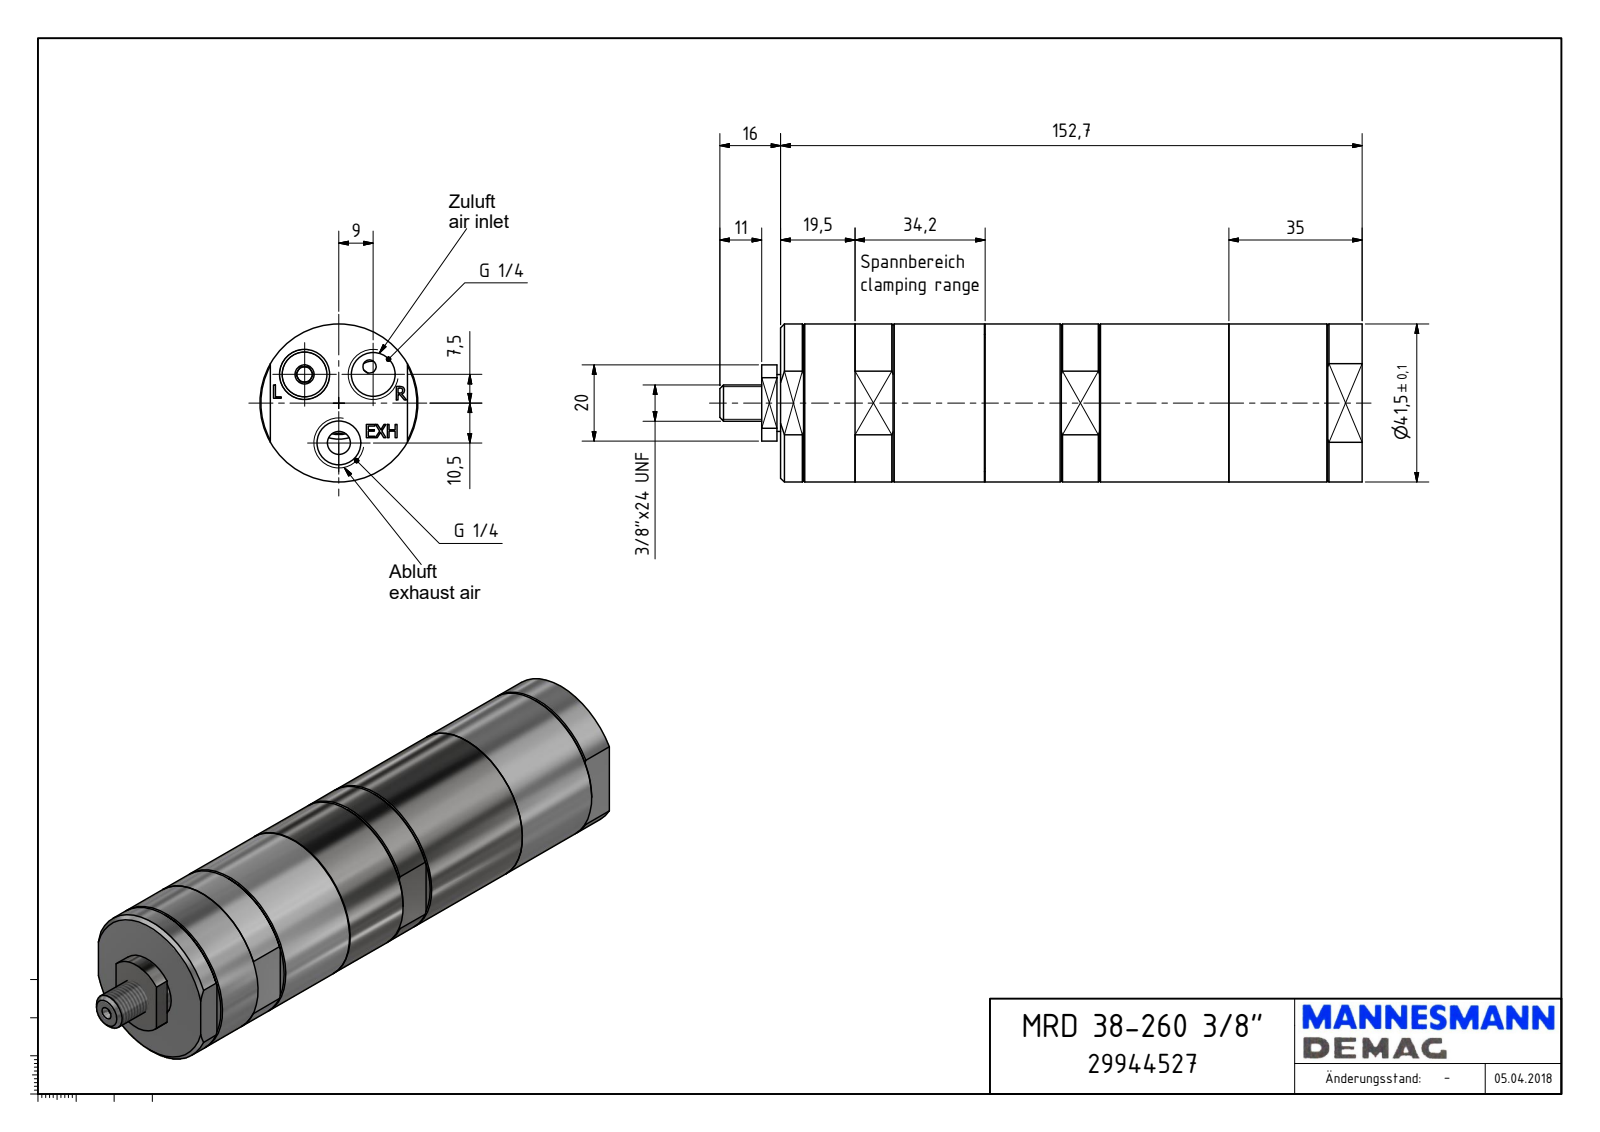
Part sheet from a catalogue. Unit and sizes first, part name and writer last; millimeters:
Units: millimetres
Overall size (bounding box): 168.7 × 41.5 × 41.5
Round holes (diameter × count): ⌀11.45 ×2, ⌀1.6 ×1, ⌀4 ×1, ⌀16 ×1, ⌀23 ×1, ⌀36.92 ×1, ⌀37.5 ×1, ⌀37.99 ×1
Round bosses / shafts (diameter × count): ⌀41.5 ×1, ⌀36.79 ×1, ⌀36 ×1, ⌀33.95 ×1, ⌀14.95 ×1, ⌀9.53 ×1
Partial cylindrical surfaces — rounded edges, fillets, slot ends (radius × count): R7 ×6, R5 ×2, R5.72 ×1, R10 ×1, R17.5 ×1
Main face-to-face distances: 152.7, 1, 38, 37, 2, 99.2, 126.7, 53.5, 53.7, 99
Hole centre spacings: 11.72, 20.12, 10.5, 18
Volume: 198 517 mm³ · Surface area: 35 019 mm²
Bodies: 1 solid, 195 faces (114 planar, 42 cylindrical, 39 other)
Part name (STEP PRODUCT): MRD 38-260 3-8_29944527
STEP written by: Autodesk Inventor 2018 (AUTOMOTIVE_DESIGN)
